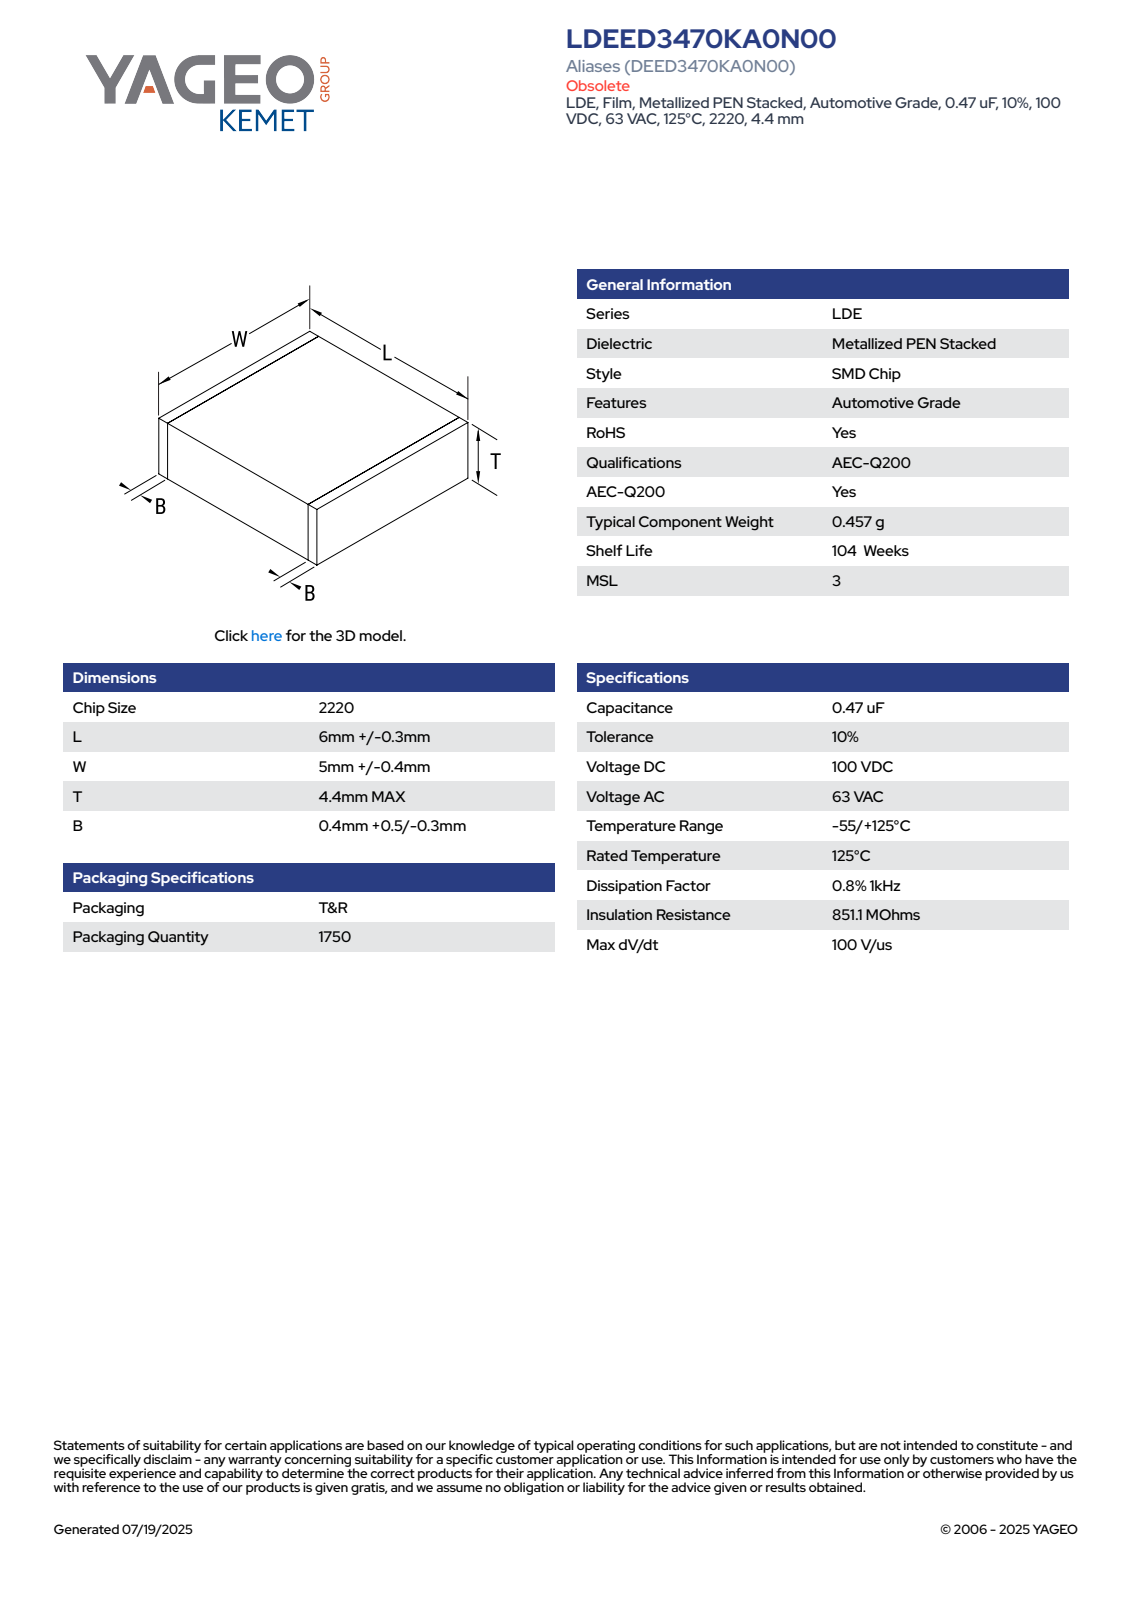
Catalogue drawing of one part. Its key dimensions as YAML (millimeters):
part_name: "CFS_LDELDB_2220_L6.3W5.4T4.4B0.9"
step_written_by: "SolidWorks 2020 (AUTOMOTIVE_DESIGN)"
units: millimeters
bodies: {solids: 4, faces: 73, planar: 73, cylindrical: 0, other: 0}
overall_size: [6.3, 5.4, 4.4]
volume: 149
surface_area: 173
face_to_face_distances: [4.38, 6.3, 5.38, 4.39, 5.39, 4.4, 5.4, 0.5, 5.8, 5.3]
